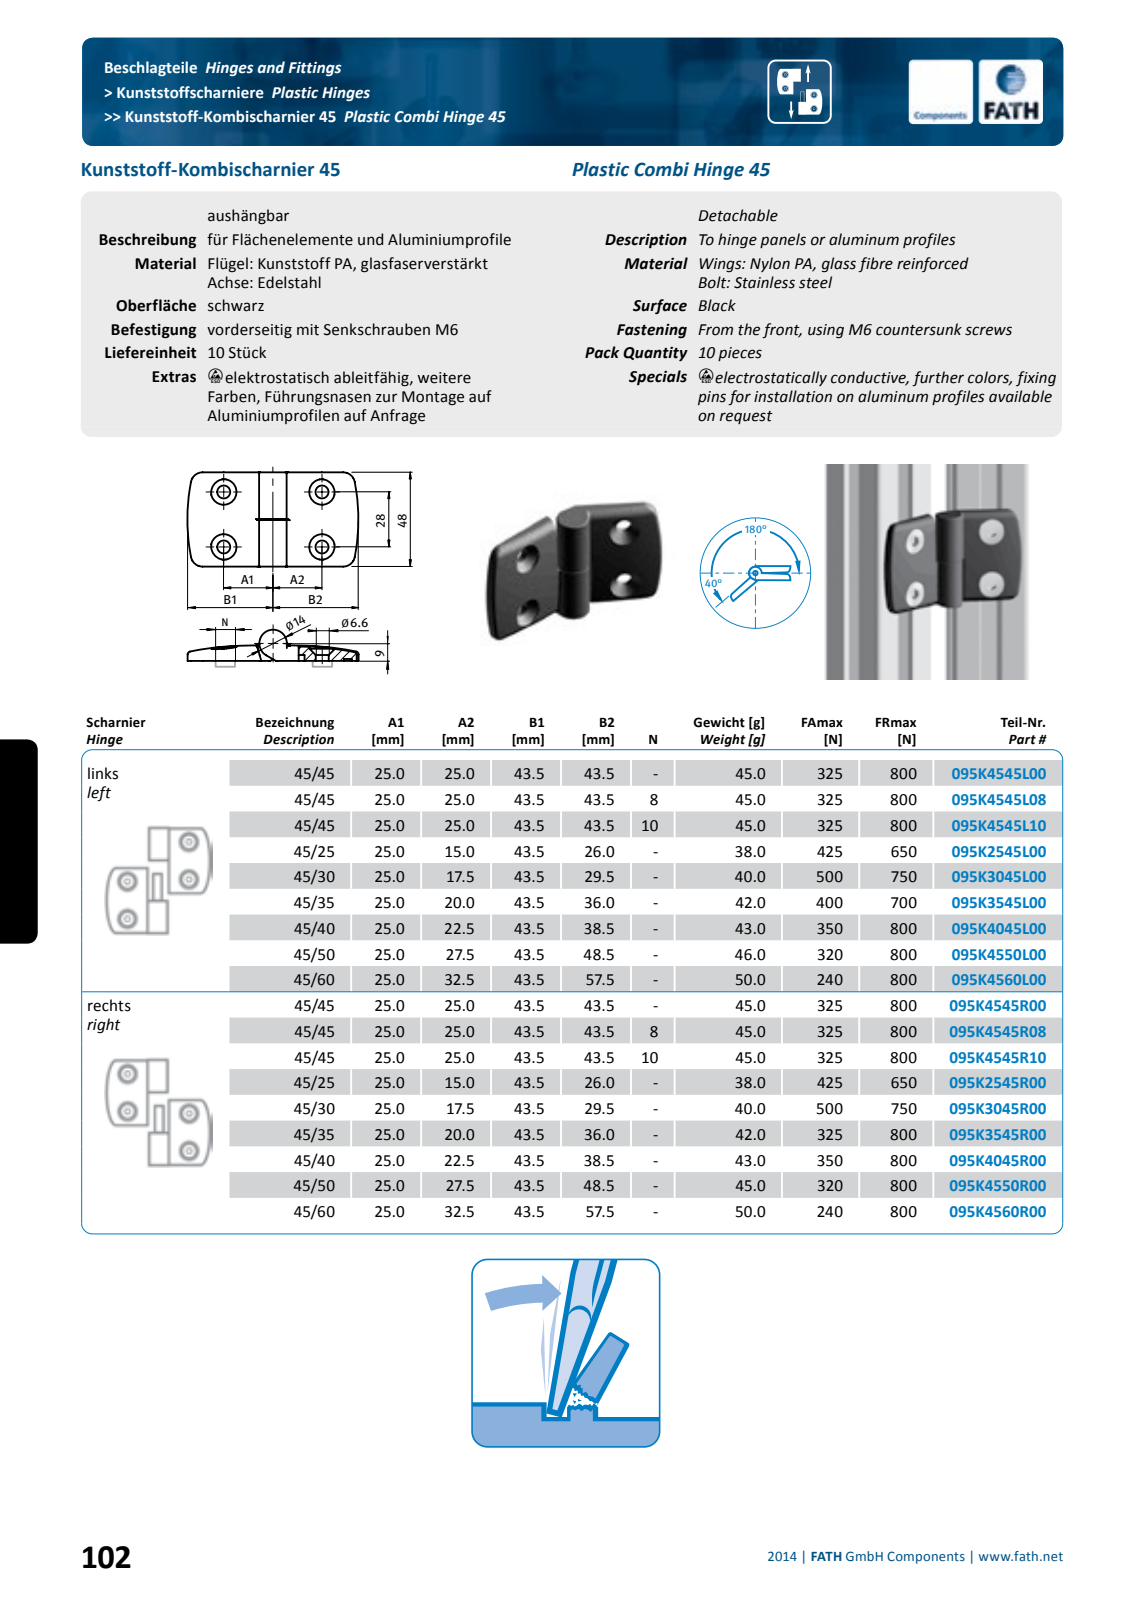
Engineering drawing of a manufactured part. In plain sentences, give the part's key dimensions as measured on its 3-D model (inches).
The part is named "fath_095k4545r10_1; fath_095k4545r10_2; fath_095k4545r10_3". Its 3-D file was written by "Spatial InterOp 3D (automotive_design)". It is 3 solids with 222 faces: 110 planar, 50 cylindrical and 62 other. Overall it measures 3.425 by 1.89 by 0.744 inches. Its volume is 1.648 cubic inches and its surface area 21.28 square inches. Round holes: 4 of diameter 0.26, 1 of diameter 0.236. Round bosses or shafts: 1 of diameter 0.551, 1 of diameter 0.244. Partial cylindrical surfaces (rounded edges, fillets, slot ends): 6 of radius 0.02, 4 of radius 0.012, 4 of radius 0.236, 4 of radius 0.256, 2 of radius 0.157, 2 of radius 3.937. The main face-to-face distances are 0.039, 0.945, 0.079, 0.118, 1.89, 0.197, 0.276, 0.866, 0.669, 0.157. The hole center spacings are 1.102, 1.969, 2.256.
